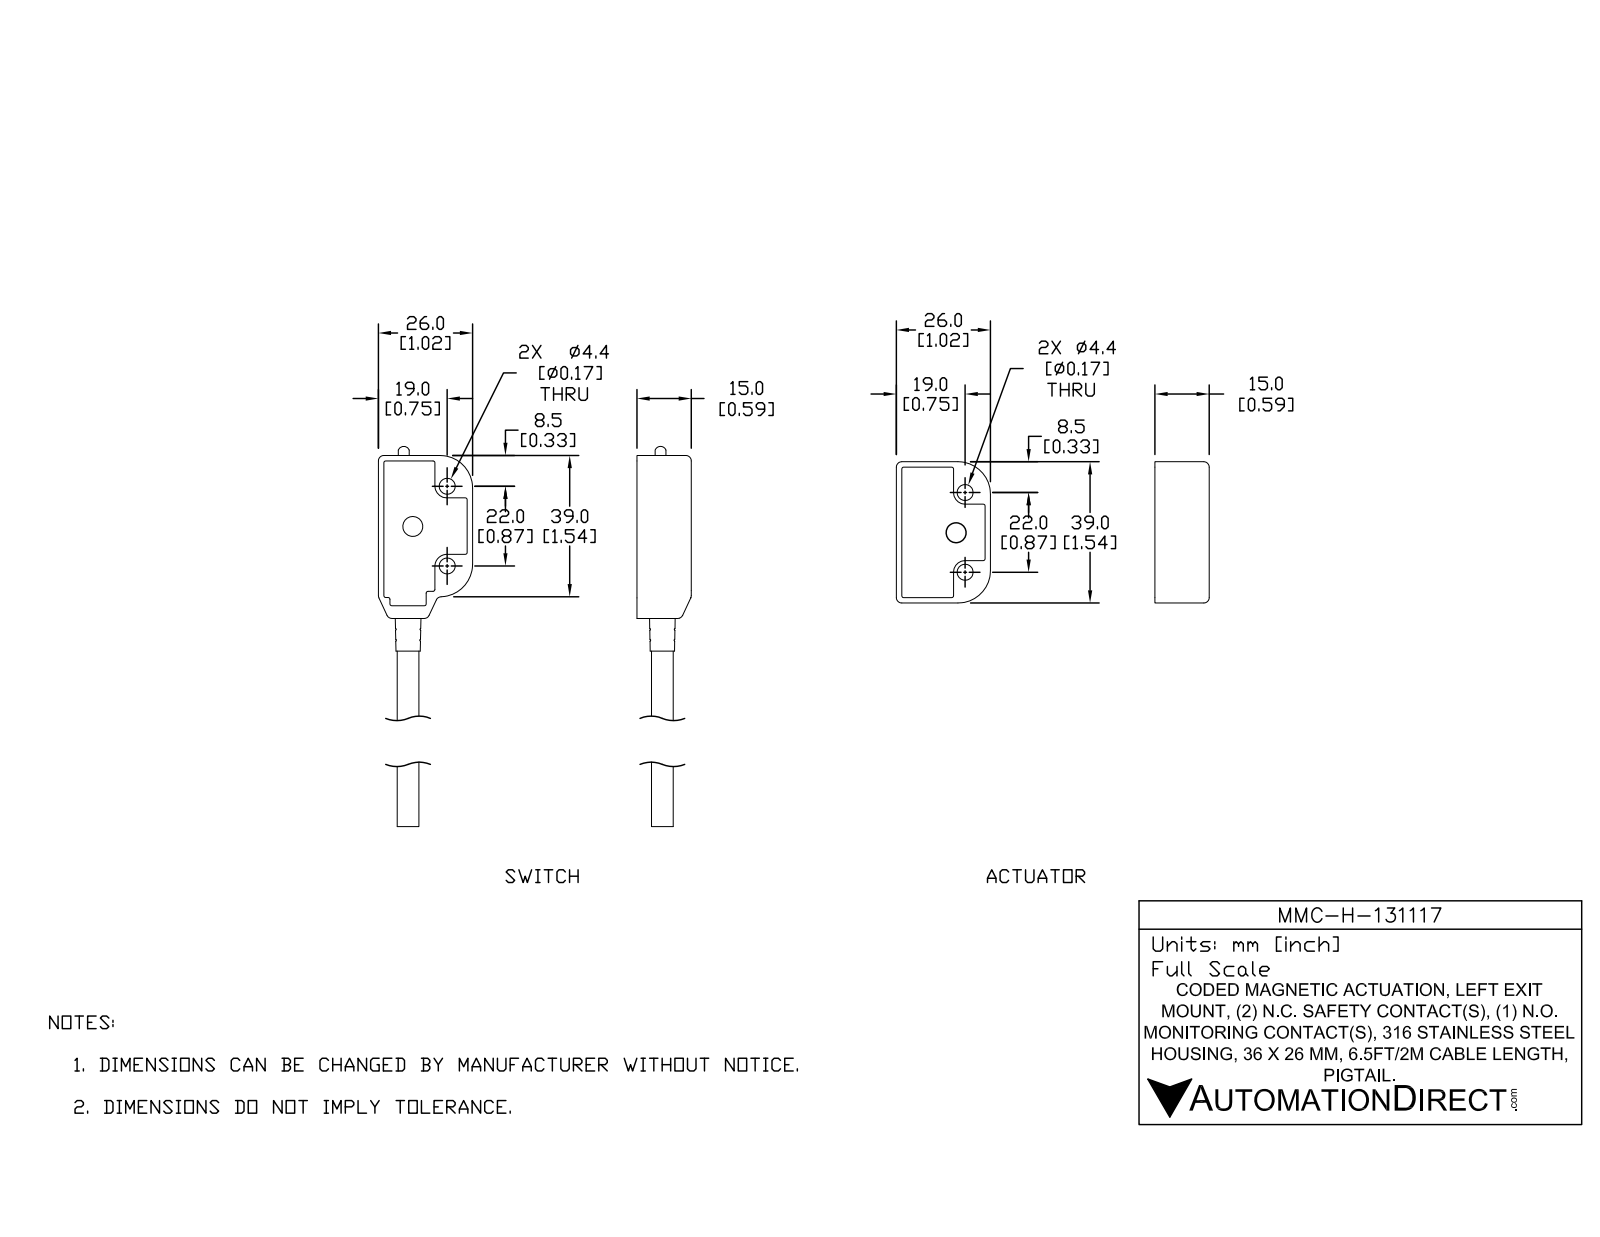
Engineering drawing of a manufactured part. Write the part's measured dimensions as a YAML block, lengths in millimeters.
part_name: "MMC-H-131117_2; MMC-H-131117; MMC-H-131117_1"
step_written_by: "SolidWorks 2017 (AUTOMOTIVE_DESIGN)"
units: millimeters
bodies: {solids: 9, faces: 603, planar: 178, cylindrical: 234, other: 191}
overall_size: [200.7, 53, 15]
volume: 20210
surface_area: 20000
round_holes:
  - {diameter: 4.4, count: 4}
  - {diameter: 5, count: 2}
  - {diameter: 3, count: 1}
  - {diameter: 5.9, count: 1}
  - {diameter: 7.2, count: 1}
round_bosses_or_shafts:
  - {diameter: 2, count: 2}
  - {diameter: 0.8, count: 2}
  - {diameter: 8.6, count: 1}
  - {diameter: 7.6, count: 1}
  - {diameter: 7.1, count: 1}
  - {diameter: 6, count: 1}
  - {diameter: 4, count: 1}
partial_cylinders:
  - {radius: 0.5, count: 83}
  - {radius: 0.3, count: 26}
  - {radius: 1.5, count: 15}
  - {radius: 0.2, count: 8}
  - {radius: 4, count: 6}
  - {radius: 3.2, count: 4}
  - {radius: 3.3, count: 4}
  - {radius: 4.6, count: 4}
face_to_face_distances: [1.5, 14.6, 13.1, 2.5, 11.7, 13.2, 1.4, 15, 13.5, 24.5]
hole_center_spacings: [14.5, 22, 31.5, 39, 44.8, 1.9, 11.2, 11.4]
